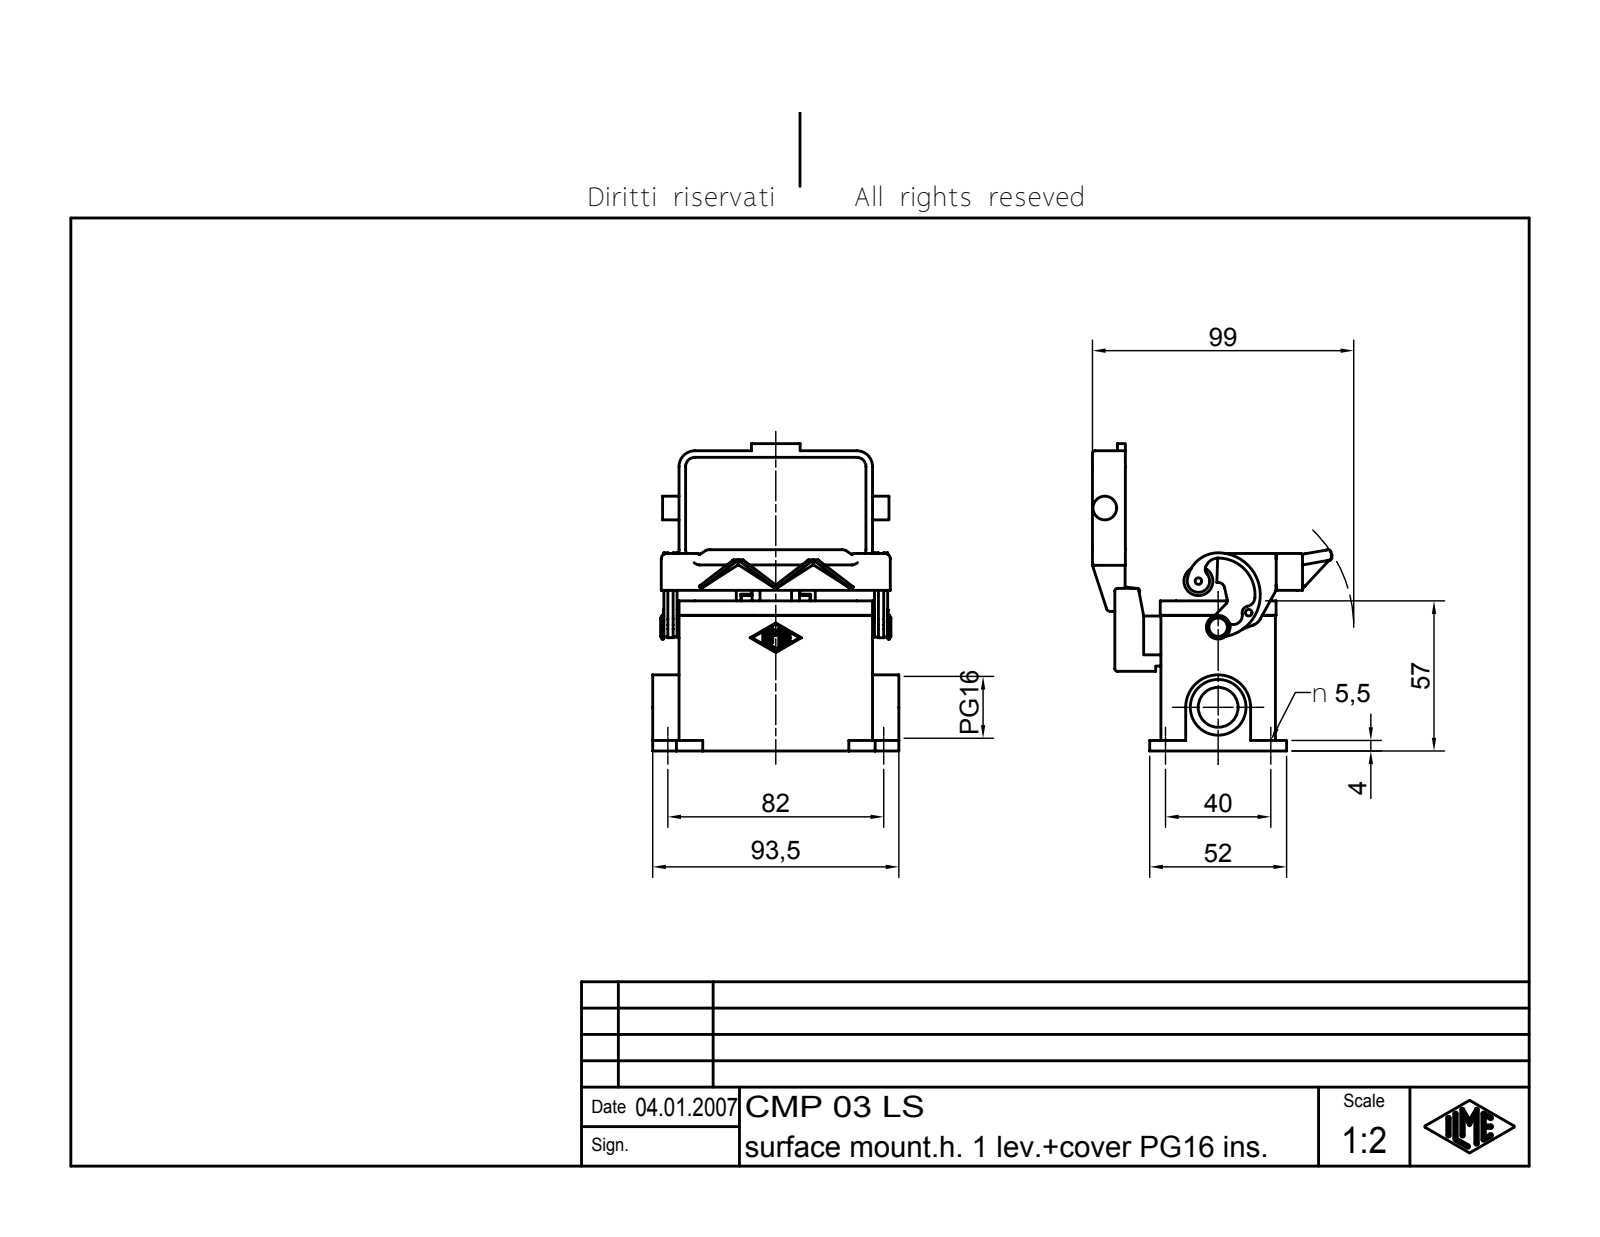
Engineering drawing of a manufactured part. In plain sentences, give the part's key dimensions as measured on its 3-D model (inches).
The part is named "CMP 03 LS". Its 3-D file was written by "Autodesk Inventor 7 (AUTOMOTIVE_DESIGN)". It is 6 solids with 592 faces: 252 planar, 180 cylindrical and 160 other. Overall it measures 4.594 by 3.681 by 3.581 inches. Its volume is 6.892 cubic inches and its surface area 99.15 square inches. Round holes: 4 of diameter 0.217, 1 of diameter 0.079, 1 of diameter 0.157, 1 of diameter 0.597, 1 of diameter 0.833. Round bosses or shafts: 2 of diameter 0.354, 2 of diameter 0.197, 1 of diameter 0.433, 1 of diameter 0.276, 1 of diameter 0.157, 1 of diameter 0.118, 1 of diameter 0.098. Partial cylindrical surfaces (rounded edges, fillets, slot ends): 18 of radius 0.039, 14 of radius 0.015, 12 of radius 0.079, 12 of radius 0.236, 6 of radius 0.059, 6 of radius 0.138, 4 of radius 0.118, 3 of radius 0.02. The main face-to-face distances are 0.118, 0.157, 1.594, 1.024, 1.713, 2.618, 2.736, 2.598, 0.138, 1.004. The hole center spacings are 1.575, 3.228, 3.592, 1.486.
